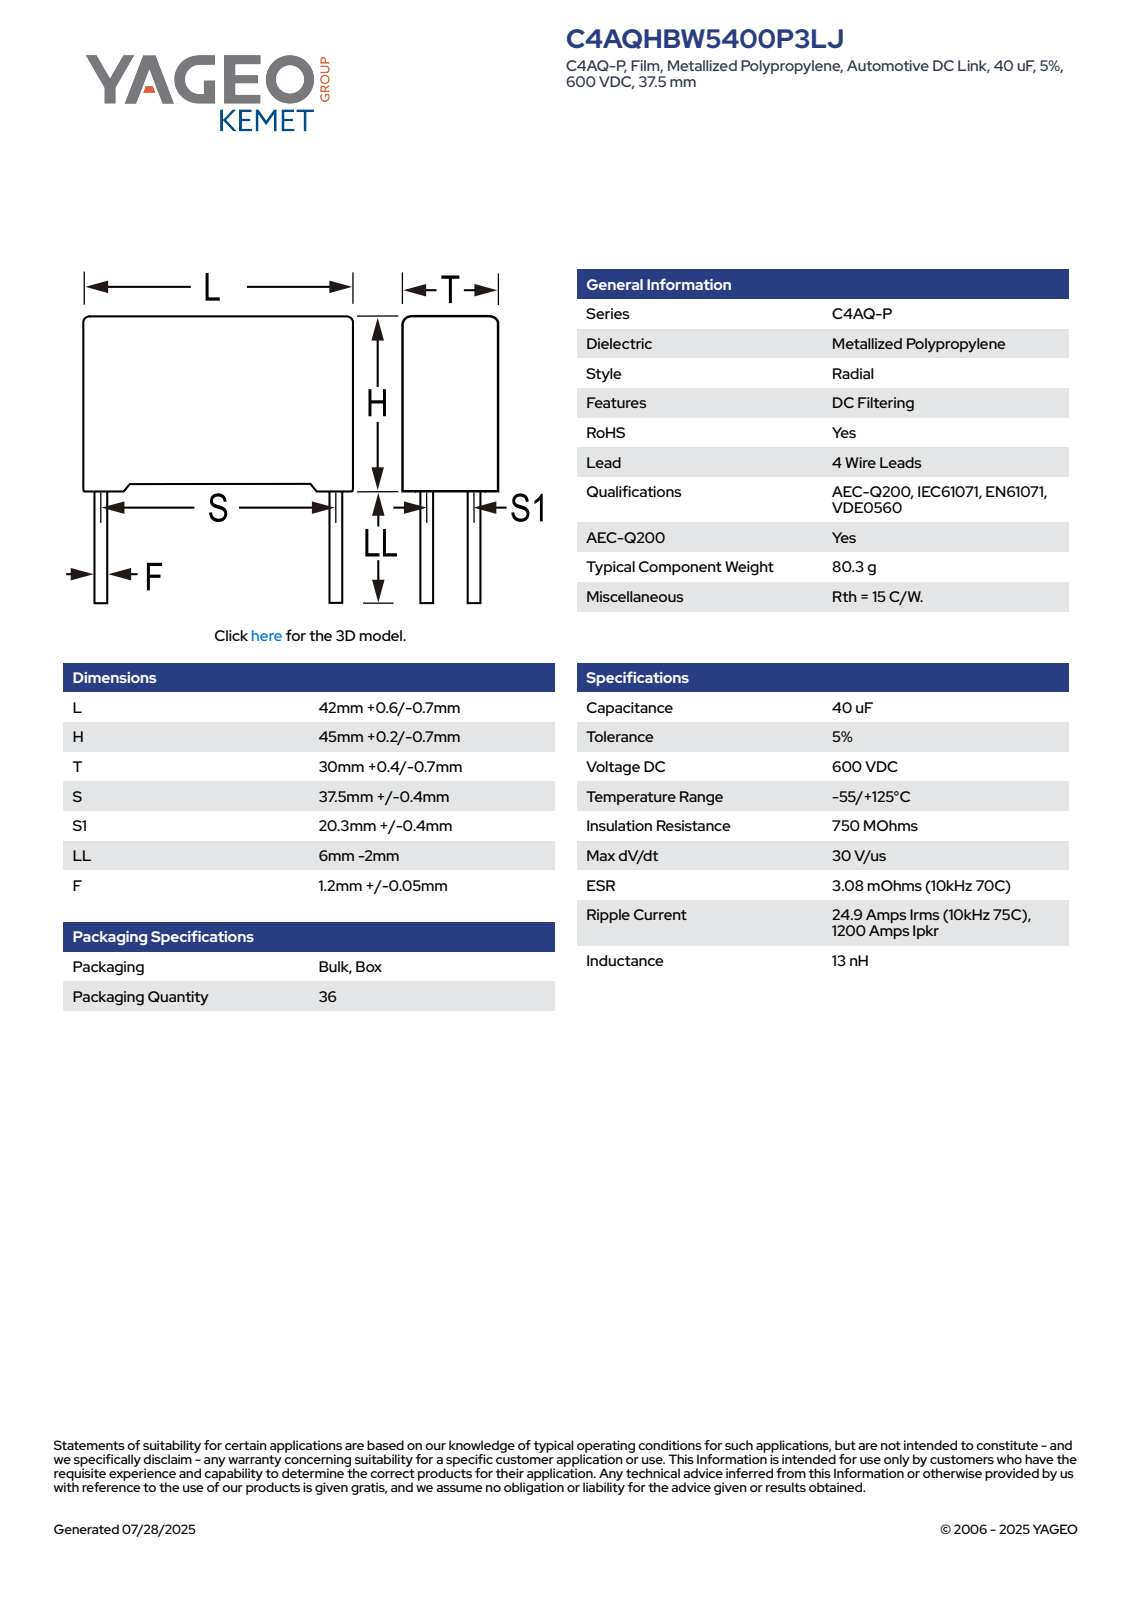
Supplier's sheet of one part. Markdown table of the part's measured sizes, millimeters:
| quantity | value |
| --- | --- |
| part name | CFP_RB4_42X45X30_L42.6H45.2T30.4S37.5S120.3LL4F1.25 |
| STEP written by | SolidWorks 2014 (AUTOMOTIVE_DESIGN) |
| units | millimeters |
| bodies | 4 solids, 87 faces (79 planar, 8 cylindrical, 0 other) |
| overall size | 49.2 × 42.6 × 30.41 |
| volume | 57 047 mm³ |
| surface area | 9 422 mm² |
| round bosses / shafts (diameter × count) | 1.25 × 4 |
| main face-to-face distances | 30.4, 42.6, 43.87, 1.33, 45.2, 1.87, 40.73, 30.41, 38.86, 28.53 |
